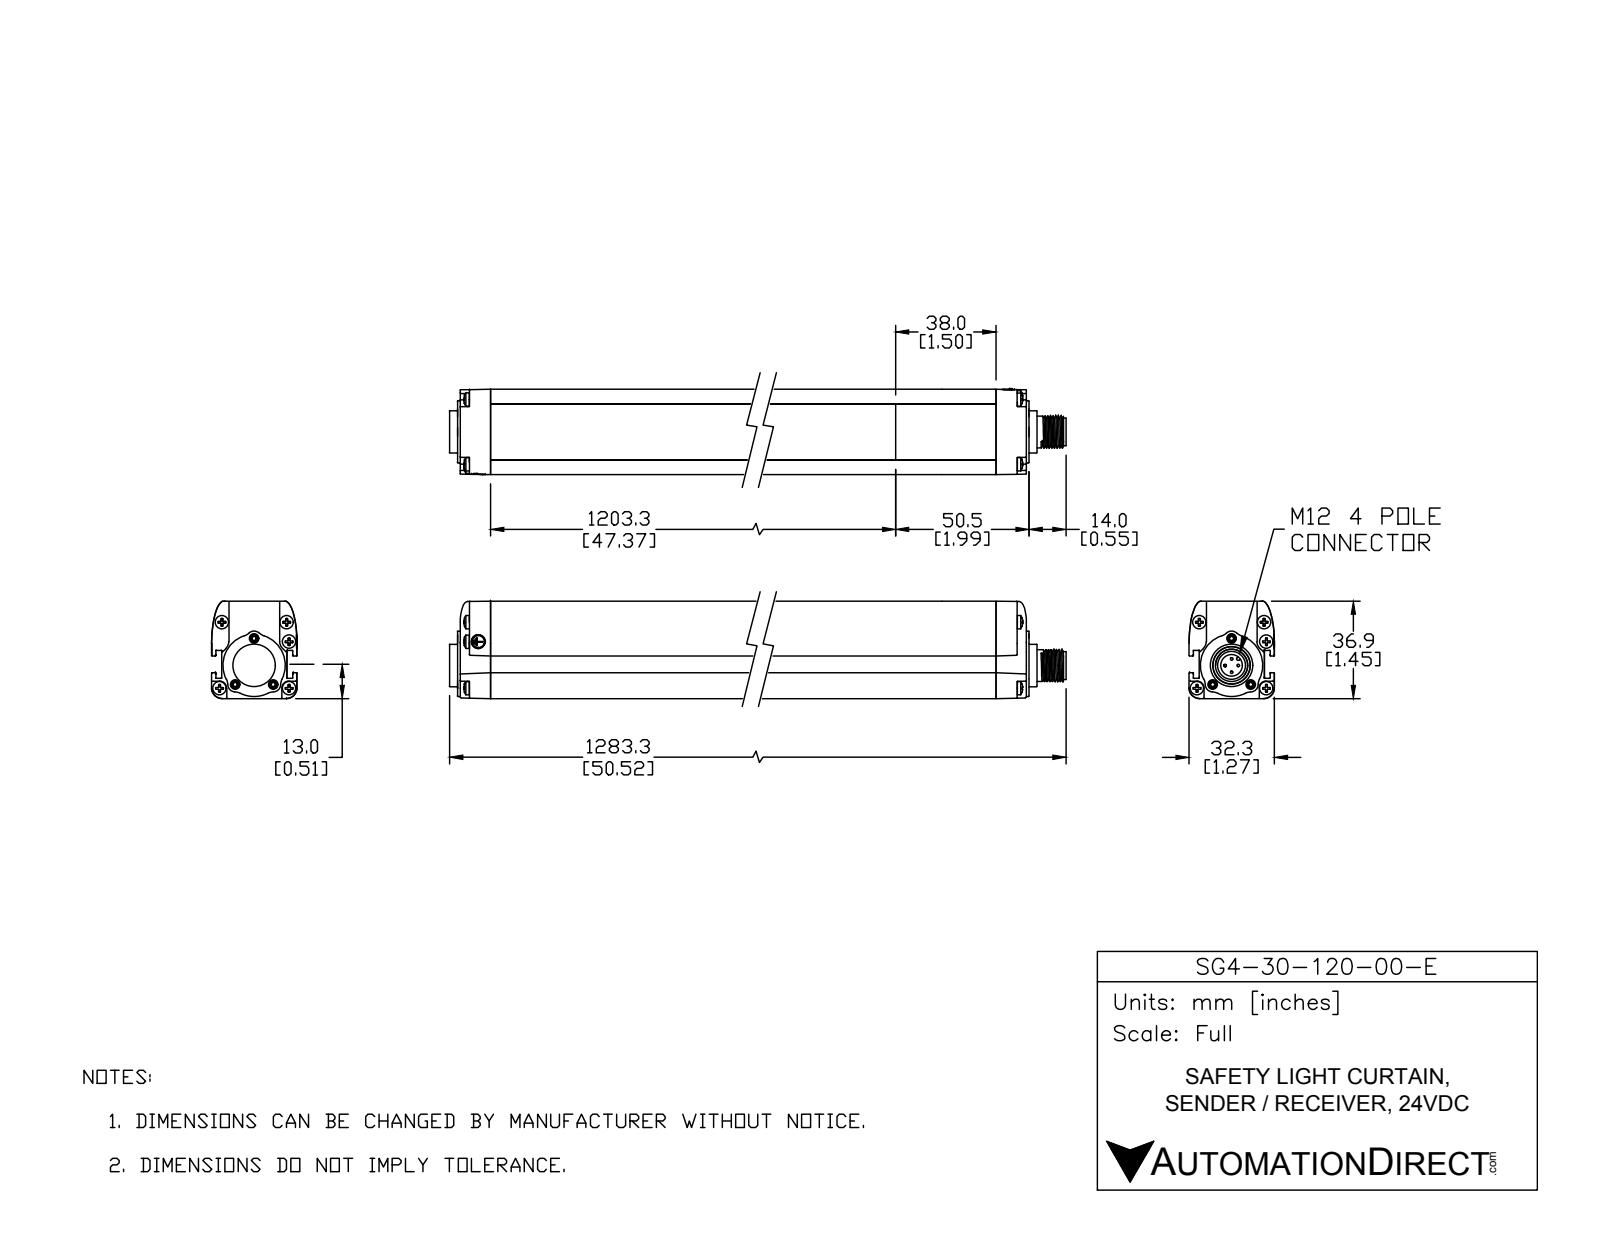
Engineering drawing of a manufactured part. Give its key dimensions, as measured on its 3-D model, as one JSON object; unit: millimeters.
{"part_name": "SG4-30-120-OO-E", "step_written_by": "SolidWorks 2017 (AUTOMOTIVE_DESIGN)", "units": "millimeters", "bodies": {"solids": 29, "faces": 1674, "planar": 410, "cylindrical": 591, "other": 673}, "overall_size": [1283.3, 63, 52.2], "volume_mm3": 1320000, "surface_area_mm2": 313100, "round_holes": [[2.7, 6], [5.3, 6], [2.1, 4], [4.2, 4], [6.6, 4], [1.5, 3], [3.6, 3], [8.2, 1], [9.6, 1], [11, 1], [14.3, 1]], "round_bosses_or_shafts": [[5, 10], [10, 4], [1, 4], [4.7, 2], [16, 1], [14, 1], [12, 1], [10.5, 1]], "partial_cylinders_radius": [[0.2, 148], [0.1, 120], [0.2, 18], [2.7, 18], [3, 8], [5, 7], [2.8, 3], [0.4, 2]], "face_to_face_distances": [2, 32.3, 36.3, 3.8, 28.5, 34.3, 4, 24.7, 8.5, 1.6], "hole_center_spacings": [14.5, 1201.3, 10.2, 6.1, 7.4, 13.2, 13.7, 15.7]}
